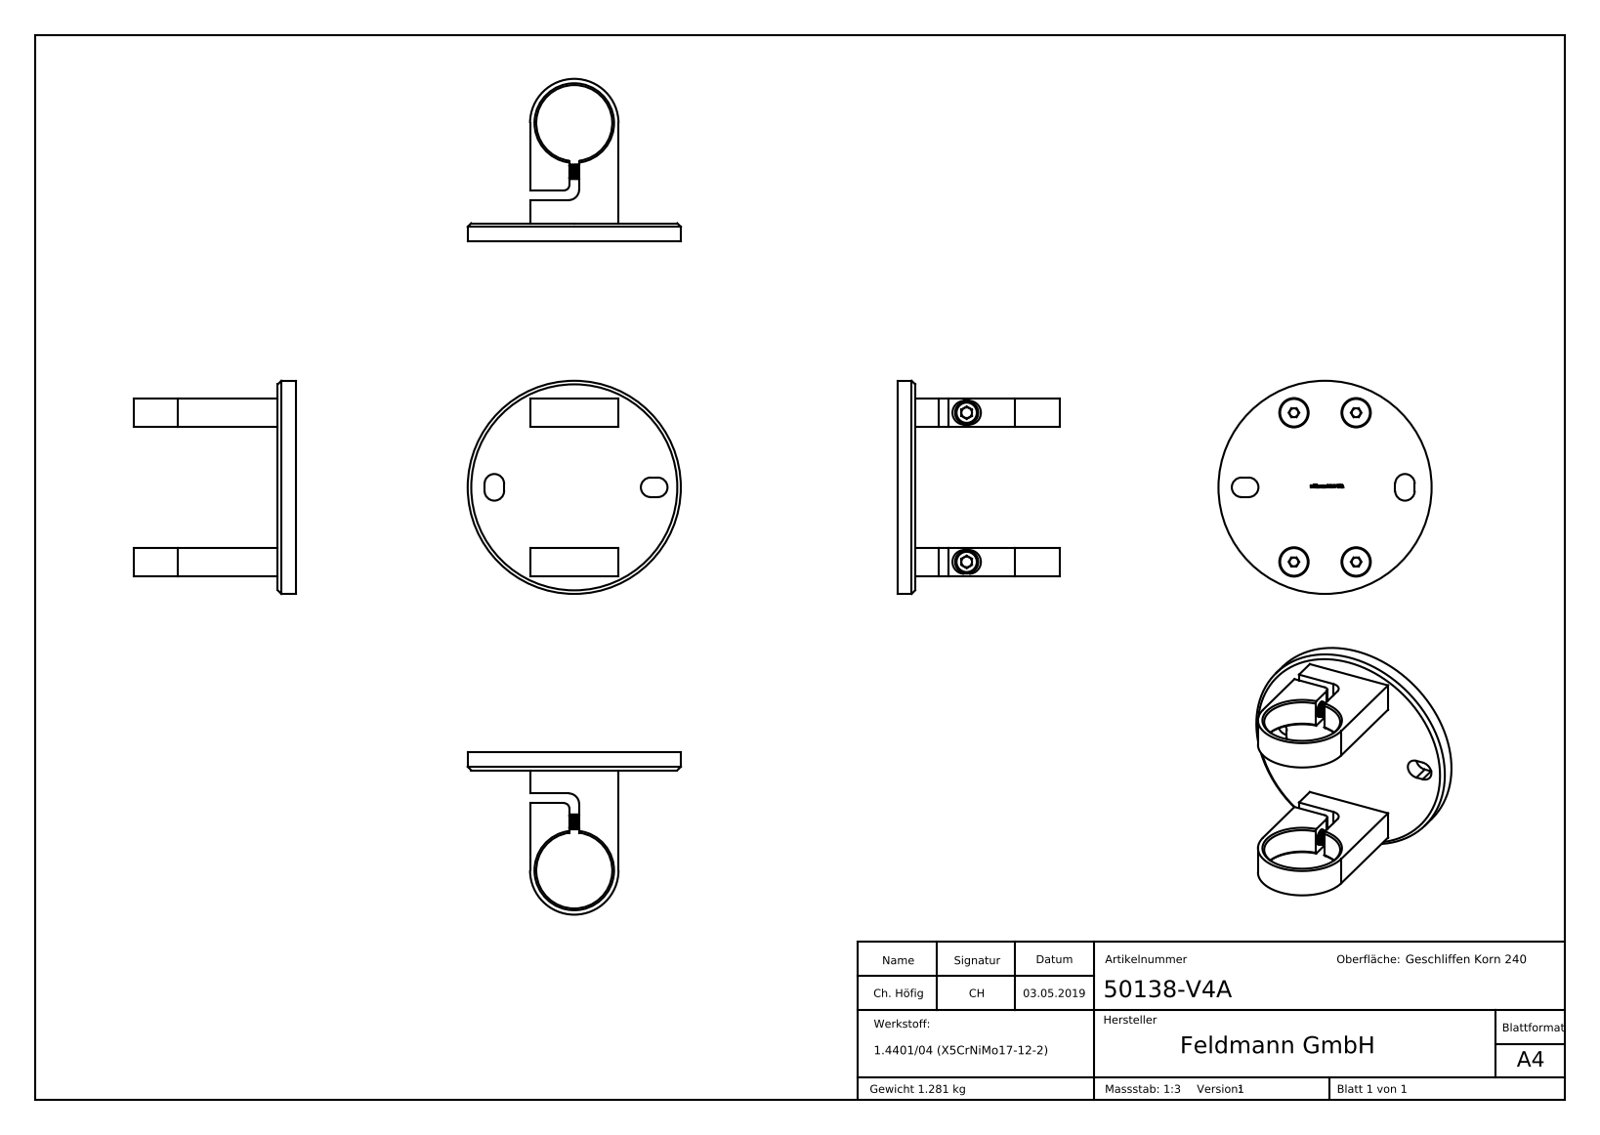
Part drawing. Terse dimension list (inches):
name: 50138-240P Konfig_50138-V4A Teil1; socket head cap screw_din_DIN 912 M8 x 30 --- 30S; 50138-V4A; 6020X-240 Teil1 Konfig_50138-V4A Teil2 (+1 more)
written by: SolidWorks 2015 (CONFIG_CONTROL_DESIGN)
unit: in
bodies: 9 solids, 1034 faces (265 planar, 251 cylindrical, 518 other)
size: 4.724 × 4.724 × 3.594
volume: 10.25 in³; area: 95.83 in²
holes: 6× ⌀0.268, 4× ⌀0.335, 4× ⌀0.65, 2× ⌀0.354, 1× ⌀1.685
bosses: 6× ⌀0.315, 4× ⌀0.613, 2× ⌀0.512, 1× ⌀4.724
rounds: 4× R0.217, 4× R0.264, 1× R0.118, 1× R0.236, 1× R0.98
face distances: 0.394, 3.307, 0.63, 3.937, 2.677, 0.512, 1.961, 0.118, 0.217, 0.852
hole spacings: 3.307, 1.378, 3.583
